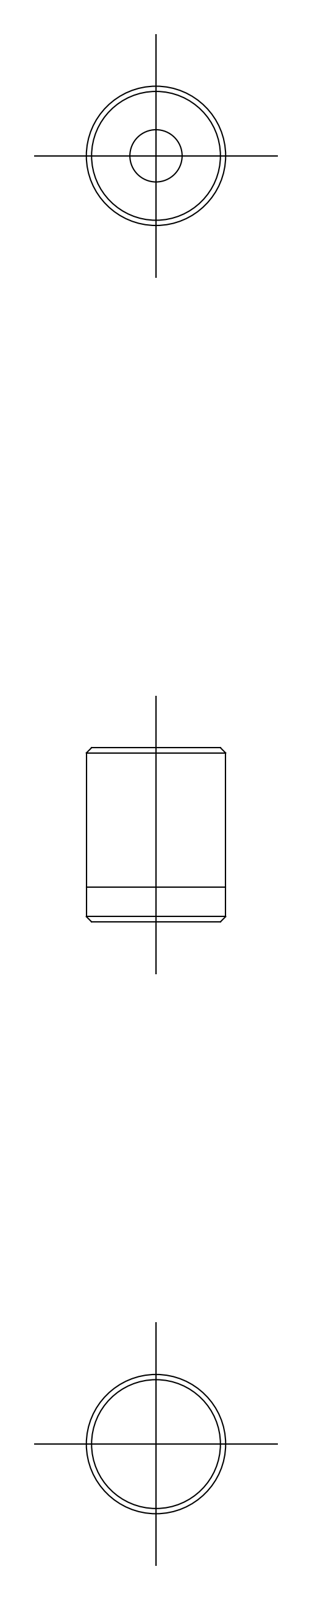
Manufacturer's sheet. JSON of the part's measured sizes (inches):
{"step_written_by": "CADfix (AUTOMOTIVE_DESIGN)", "units": "inches", "bodies": {"solids": 1, "faces": 16, "planar": 0, "cylindrical": 0, "other": 16}, "overall_size": [0.394, 0.315, 0.315], "volume_in3": 0.03, "surface_area_in2": 0.558}
